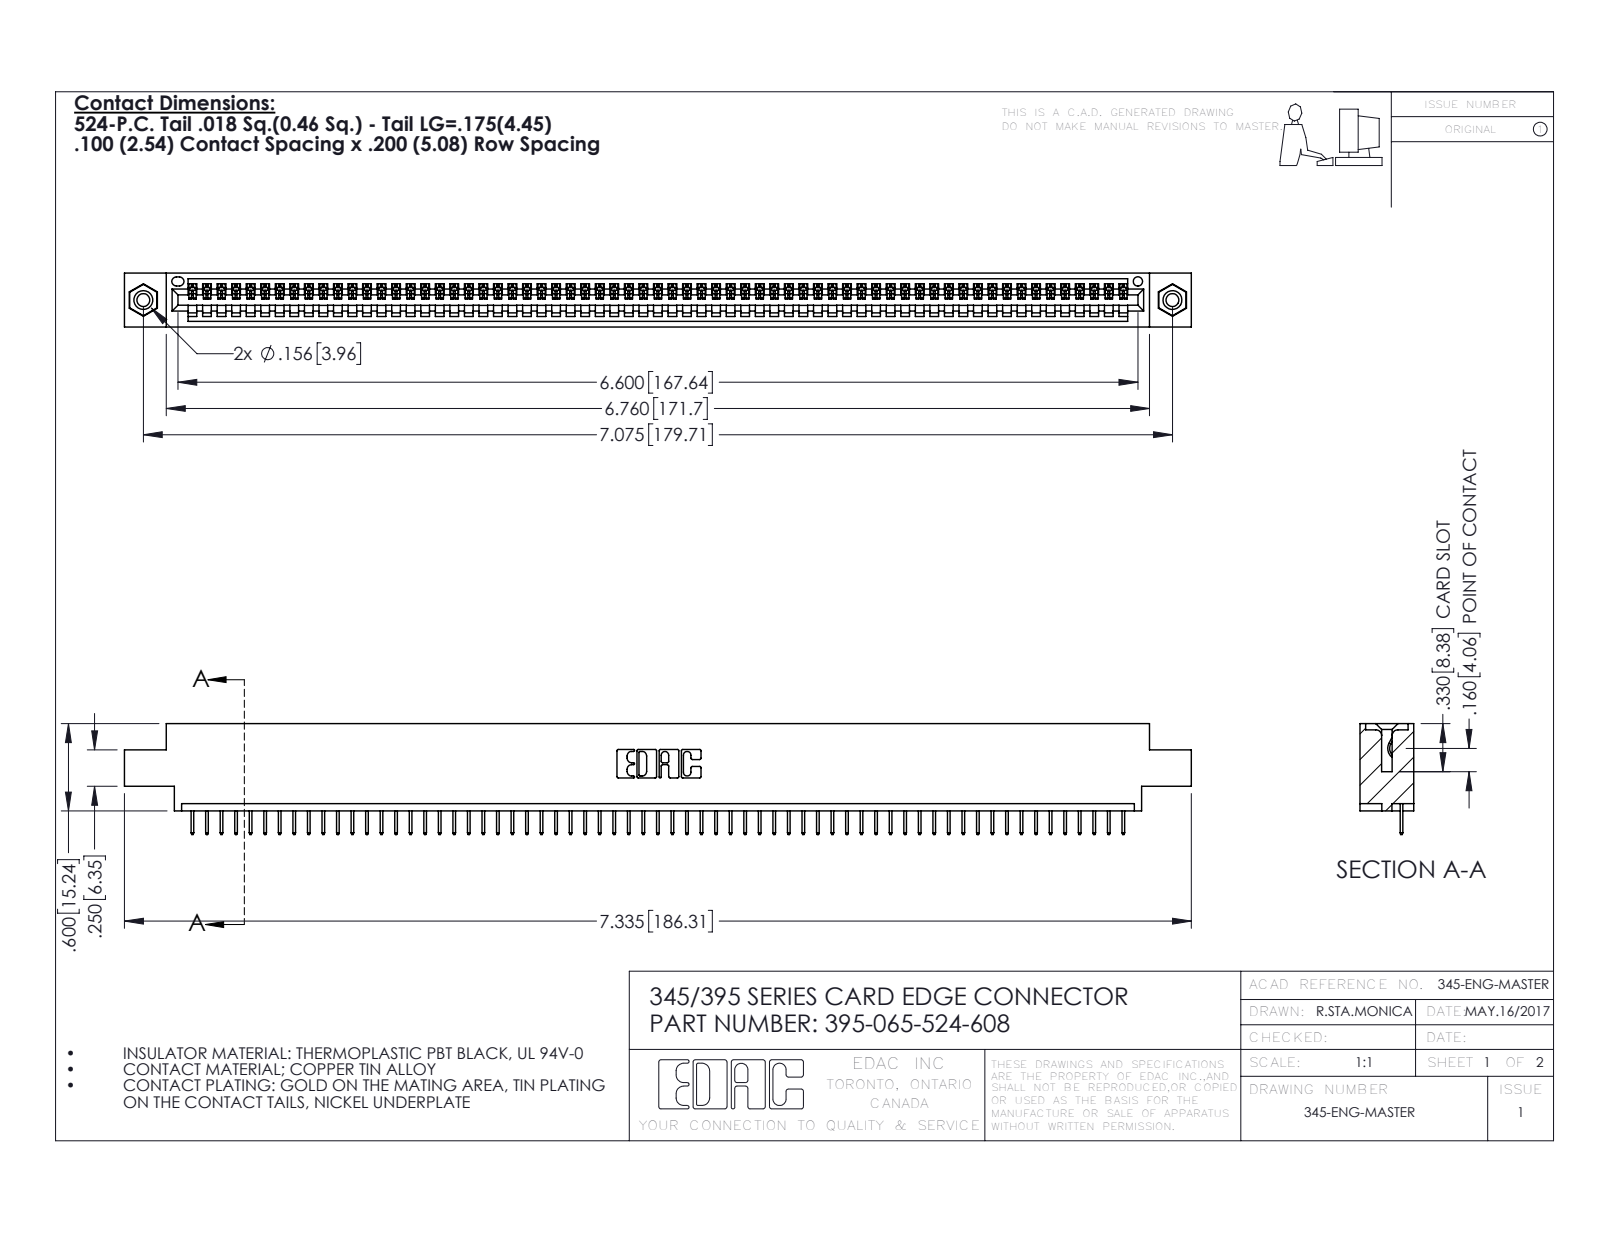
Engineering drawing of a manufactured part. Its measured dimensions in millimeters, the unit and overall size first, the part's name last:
Units: millimetres
Overall size (bounding box): 186.3 × 19.4 × 9.4
Round holes (diameter × count): ⌀2.3 ×2, ⌀3.2 ×2, ⌀4 ×2, ⌀1.6 ×1
Round bosses / shafts (diameter × count): ⌀3.9 ×2
Partial cylindrical surfaces — rounded edges, fillets, slot ends (radius × count): R0.2 ×130, R0.3 ×22, R0.2 ×6, R0.8 ×6, R0.7 ×3, R0.8 ×2, R1 ×2, R0.4 ×1
Main face-to-face distances: 1.8, 7.6, 9.4, 5.1, 2.5, 6.9, 0.6, 5.7, 1.8, 4.4
Hole centre spacings: 6.9, 173.7, 179.7
Volume: 17 500 mm³ · Surface area: 22 900 mm²
Bodies: 68 solids, 4220 faces (3106 planar, 1098 cylindrical, 16 other)
Part name (STEP PRODUCT): 345-292-001_345-293-124; 345 Part_0.170 Offset - 0.156 Dia-TI; 395-065-524-608; 345-250-001_345-250-003-102
STEP written by: SolidWorks 2016 (CONFIG_CONTROL_DESIGN)
